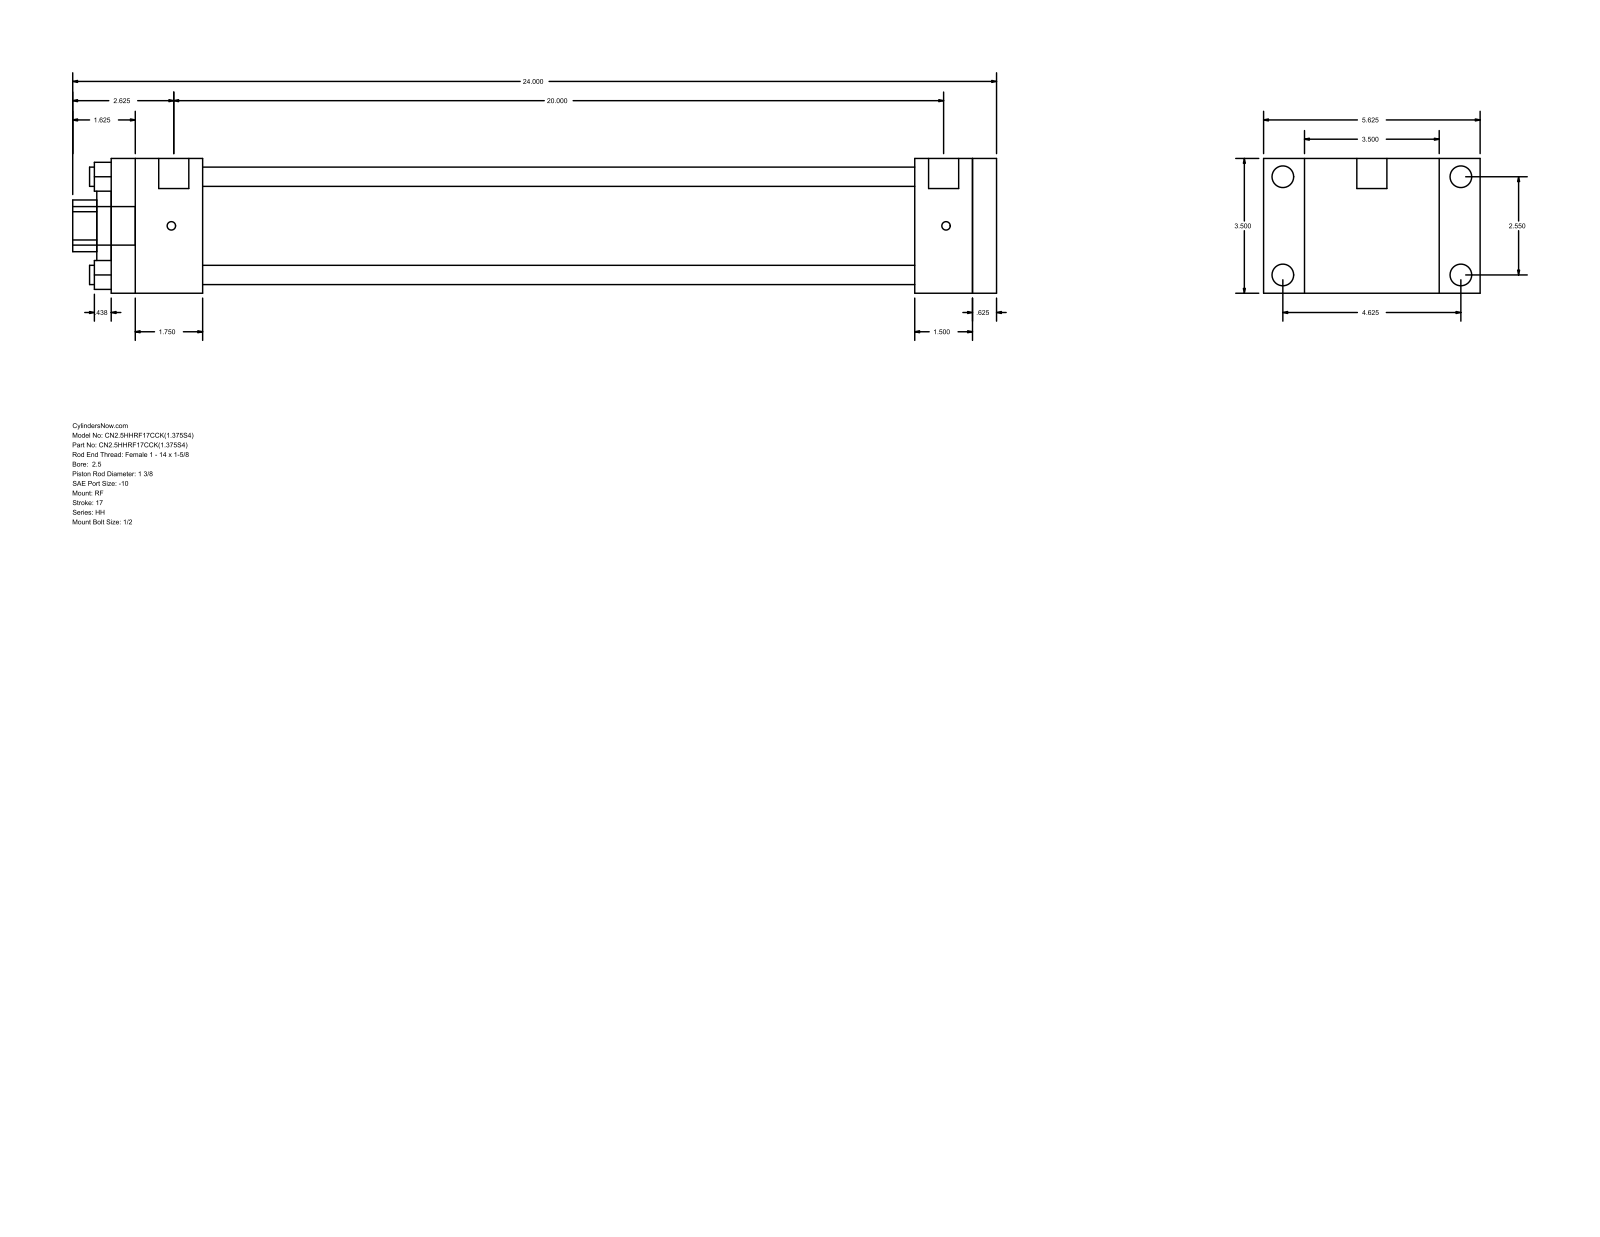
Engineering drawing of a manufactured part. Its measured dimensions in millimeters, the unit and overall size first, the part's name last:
Units: millimetres
Overall size (bounding box): 609.6 × 142.88 × 88.9
Round holes (diameter × count): ⌀12.7 ×4, ⌀34.92 ×1, ⌀50.8 ×1, ⌀73.03 ×1
Round bosses / shafts (diameter × count): ⌀14.3 ×4, ⌀5.56 ×4, ⌀19.84 ×2, ⌀25.4 ×1
Partial cylindrical surfaces — rounded edges, fillets, slot ends (radius × count): R17.06 ×1
Main face-to-face distances: 88.9, 15.87, 568.33, 584.2, 60.32, 508.01, 523.88, 530.22, 469.9, 38.11
Hole centre spacings: 45.79, 64.76, 91.58
Bodies: 0 solids, 92 faces (64 planar, 28 cylindrical, 0 other)
Part name (STEP PRODUCT): HH_RF__0250_1.375
STEP written by: GSSL Pune (CONFIG_CONTROL_DESIGN)
